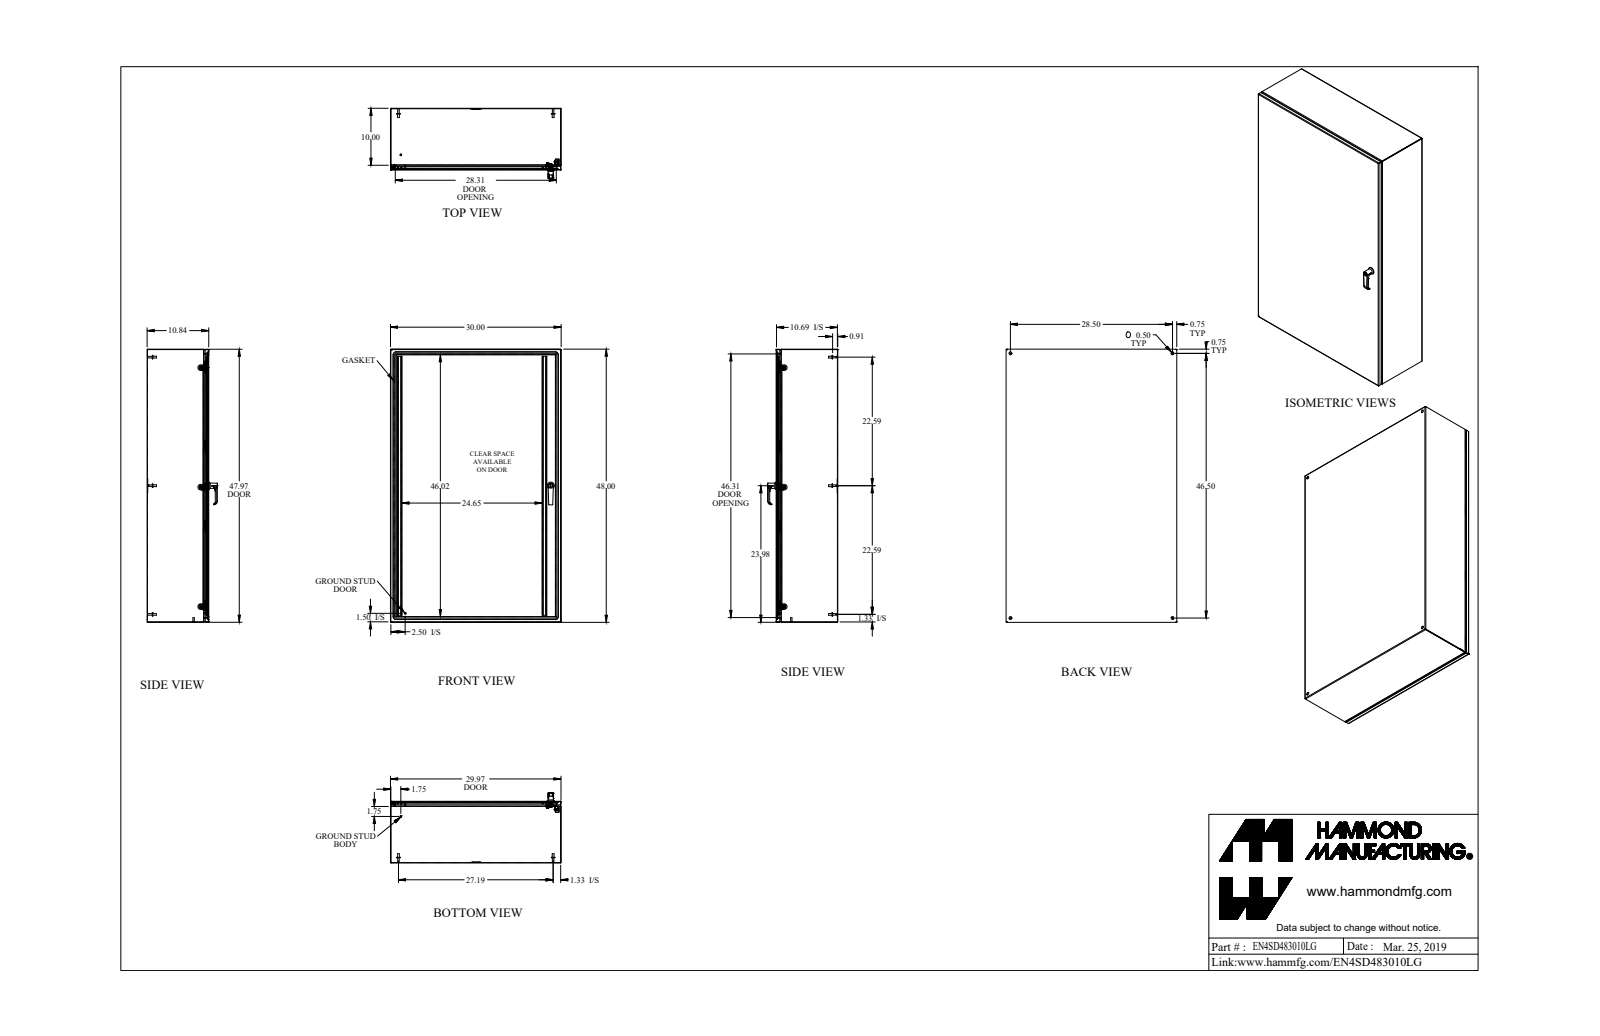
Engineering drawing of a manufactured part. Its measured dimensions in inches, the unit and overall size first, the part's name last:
Units: inches
Overall size (bounding box): 48 × 30 × 12.367
Round holes (diameter × count): ⌀0.176 ×6, ⌀0.5 ×4, ⌀0.196 ×3, ⌀0.25 ×3, ⌀0.265 ×3, ⌀0.413 ×3, ⌀0.256 ×2, ⌀0.313 ×2, ⌀0.394 ×2, ⌀0.172 ×1, ⌀0.24 ×1, ⌀0.242 ×1
Round bosses / shafts (diameter × count): ⌀0.25 ×7, ⌀0.375 ×6, ⌀0.156 ×6, ⌀0.625 ×5, ⌀0.313 ×5, ⌀0.27 ×5, ⌀1 ×3, ⌀0.63 ×2
Partial cylindrical surfaces — rounded edges, fillets, slot ends (radius × count): R0.036 ×20, R0.108 ×20, R0.03 ×15, R0.043 ×12, R0.081 ×12, R0.006 ×8, R0.04 ×8, R0.062 ×8
Main face-to-face distances: 0.072, 10.765, 10.693, 10.837, 29.928, 29.856, 30, 0.072, 47.928, 47.856
Hole centre spacings: 41.969, 0.787, 20.981, 20.988, 21, 27.52, 28.5, 46.5
Volume: 372.3 in³ · Surface area: 10 334 in²
Bodies: 52 solids, 1441 faces (628 planar, 532 cylindrical, 281 other)
Part name (STEP PRODUCT): EN4SD483010LG
STEP written by: SolidWorks 2018 (AUTOMOTIVE_DESIGN)
